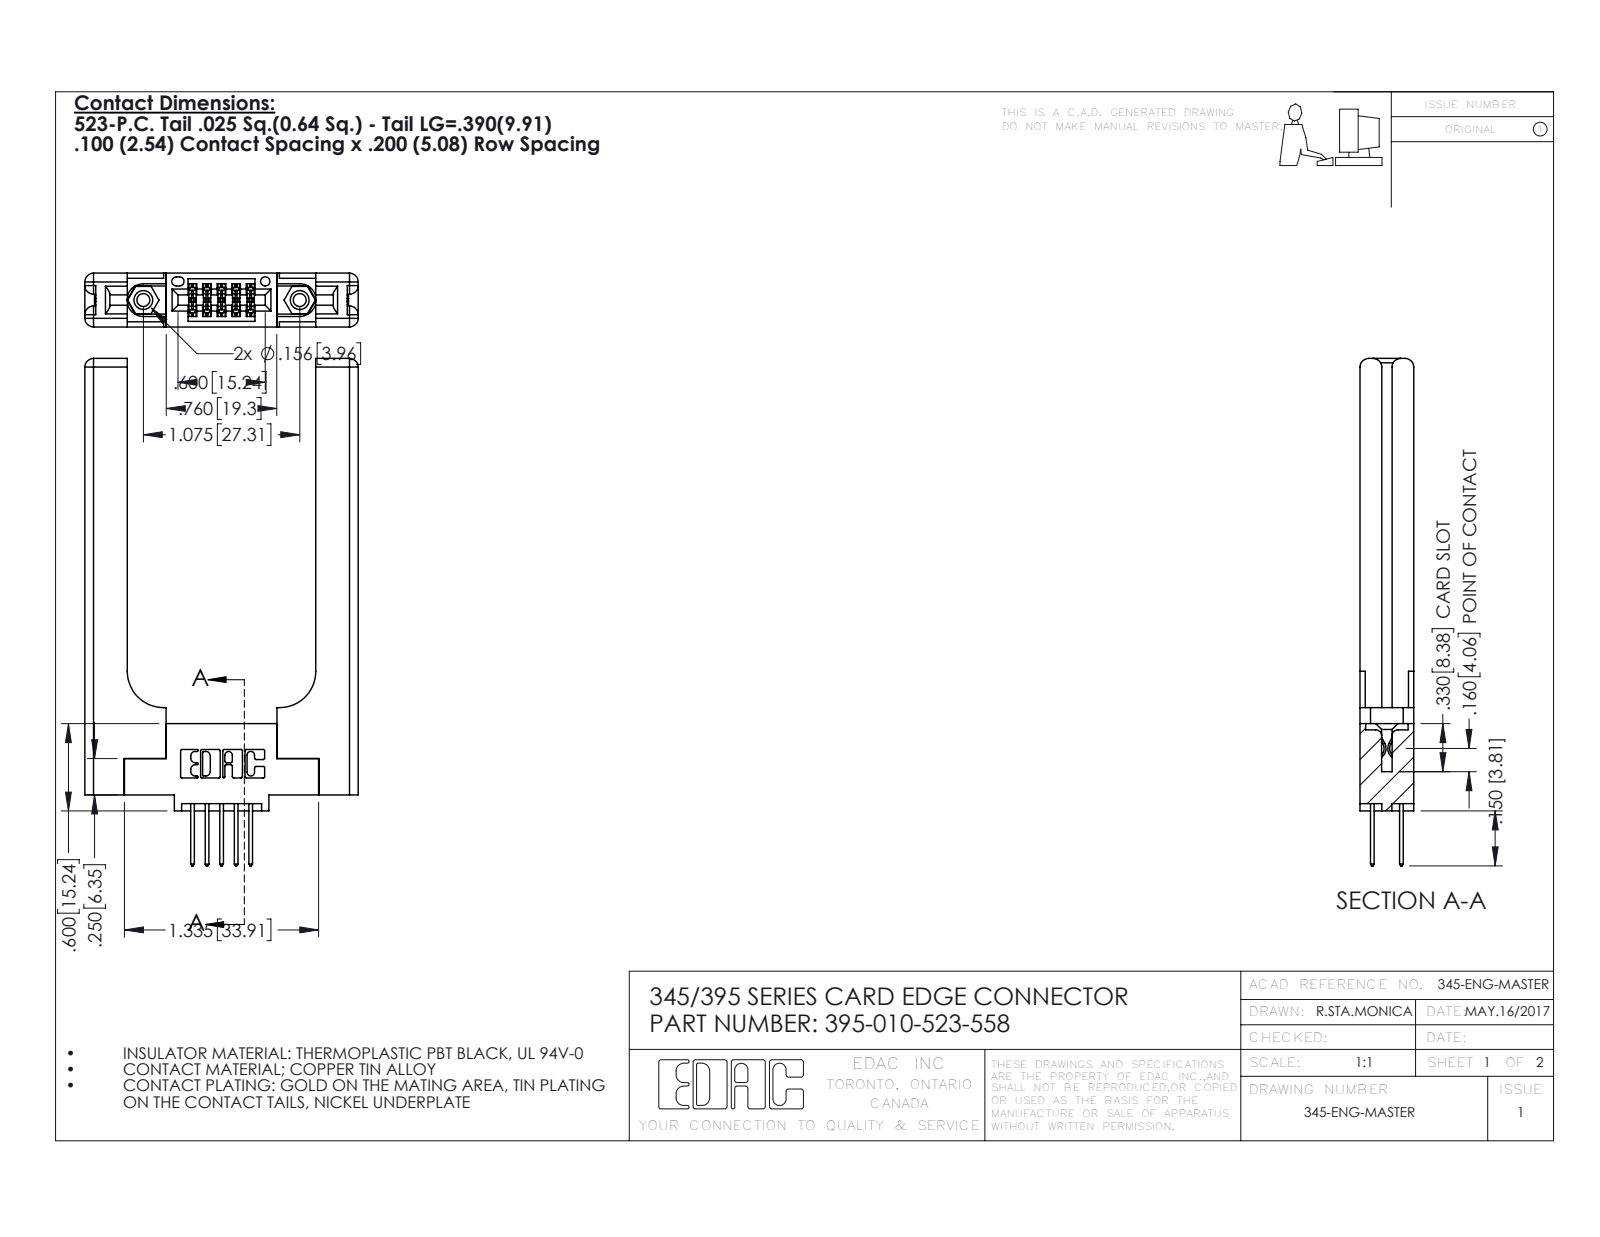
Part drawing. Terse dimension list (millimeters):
name: 345-250-001_345-250-001-102; 345 Part_0.110 Offset - 0.156 Dia-TH; 345-292-001_345-293-123; 395-010-523-558 (+1 more)
written by: SolidWorks 2016 (CONFIG_CONTROL_DESIGN)
unit: mm
bodies: 15 solids, 886 faces (562 planar, 264 cylindrical, 60 other)
size: 88.6 × 47.7 × 9.4
volume: 12 700 mm³; area: 10 790 mm²
holes: 2× ⌀2.3, 2× ⌀3.2, 2× ⌀4, 1× ⌀1.6
bosses: 2× ⌀3.9
rounds: 22× R0.3, 16× R1.5, 15× R0.2, 10× R0.3, 6× R0.2, 6× R0.8, 3× R0.7, 2× R0.4
face distances: 9.4, 3.8, 5.6, 1.8, 3.8, 2, 32.9, 7.6, 1.8, 7.4
hole spacings: 6.9, 21.5, 27.3
